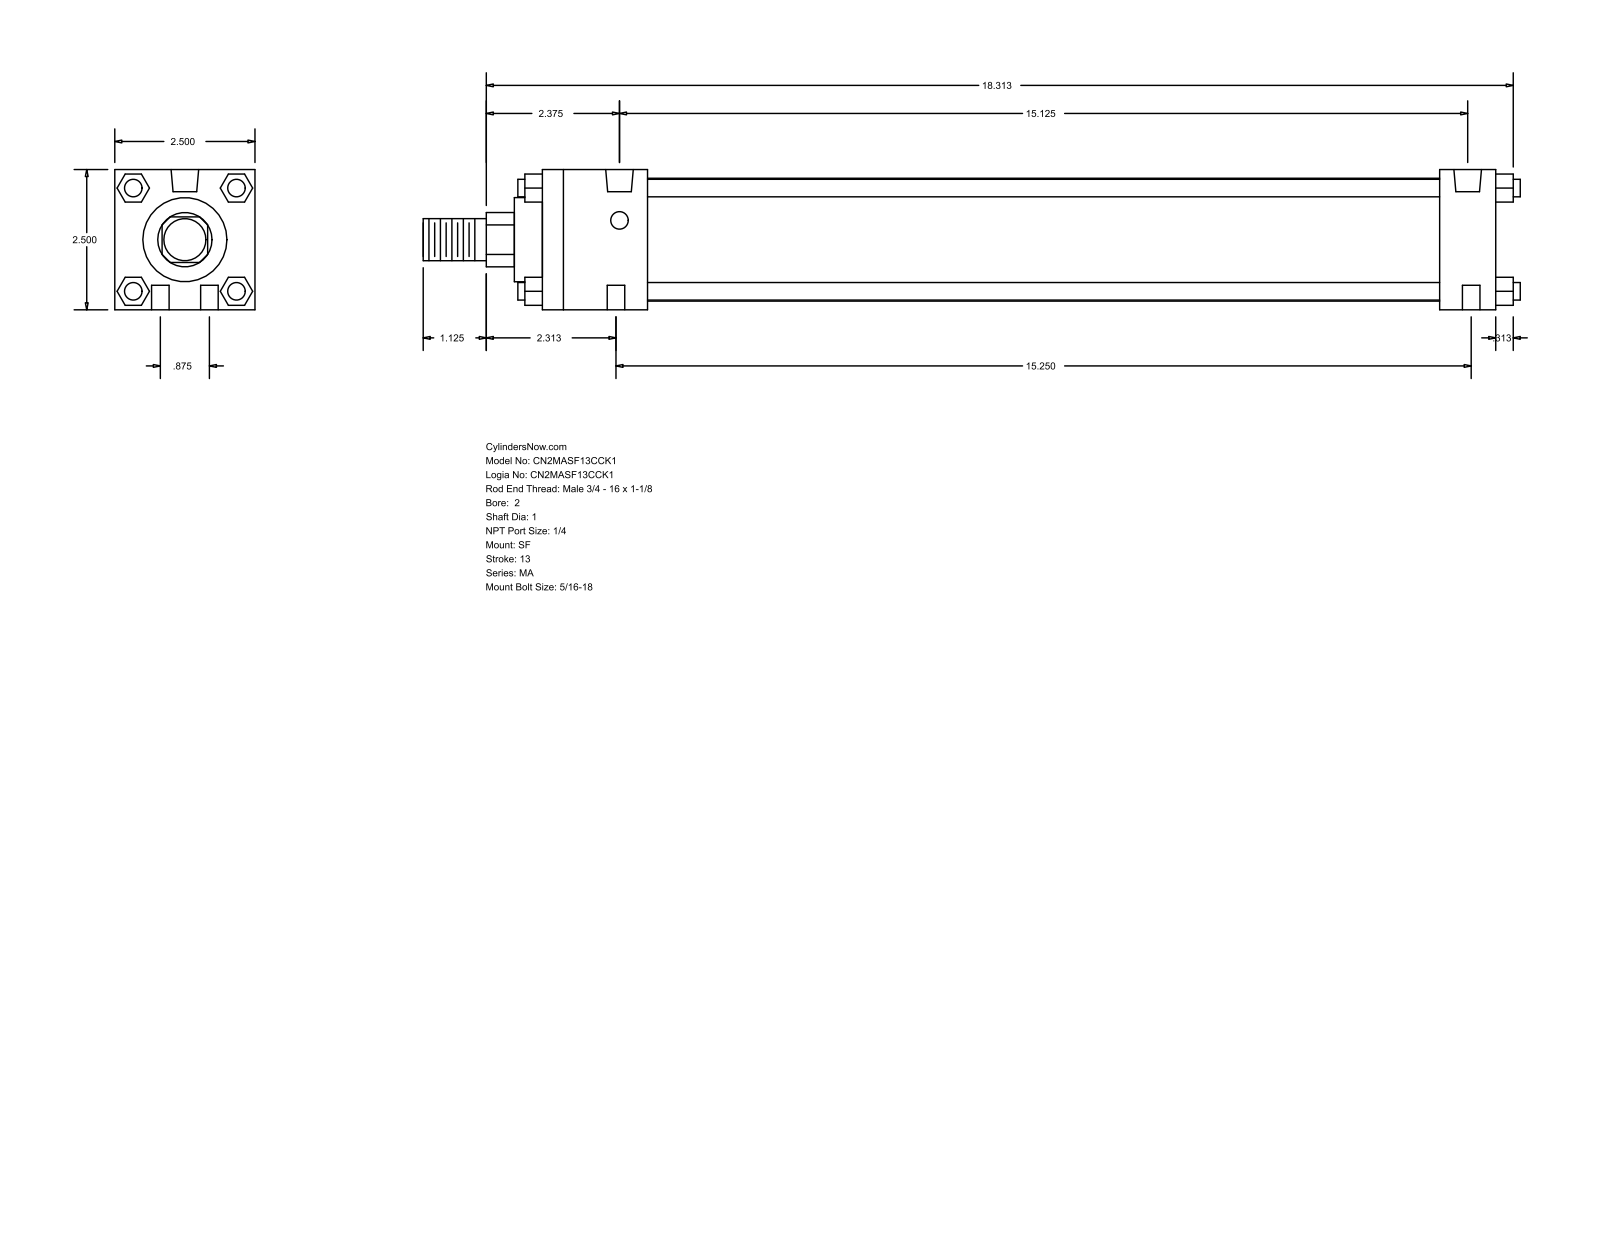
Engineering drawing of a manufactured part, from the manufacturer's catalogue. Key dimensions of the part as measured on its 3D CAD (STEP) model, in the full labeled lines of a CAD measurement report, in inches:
Part name (STEP PRODUCT): MA_SF__0200_1
STEP written by: GSSL Pune (CONFIG_CONTROL_DESIGN)
Units: inches
Bodies: 0 solids, 124 faces (94 planar, 30 cylindrical, 0 other)
Overall size (bounding box): 19.563 × 2.5 × 2.5
Round holes (diameter × count): ⌀0.313 ×6, ⌀0.492 ×2
Round bosses / shafts (diameter × count): ⌀0.313 ×4, ⌀2.19 ×1, ⌀1.5 ×1, ⌀1 ×1, ⌀0.75 ×1
Partial cylindrical surfaces — rounded edges, fillets, slot ends (radius × count): R0.484 ×1
Main face-to-face distances: 2.5, 17, 0.5, 1, 16, 1.875, 14.125, 15.125, 1.593, 0.92
Hole centre spacings: 0.442, 15.194, 0.875, 15.125, 15.25, 15.275
